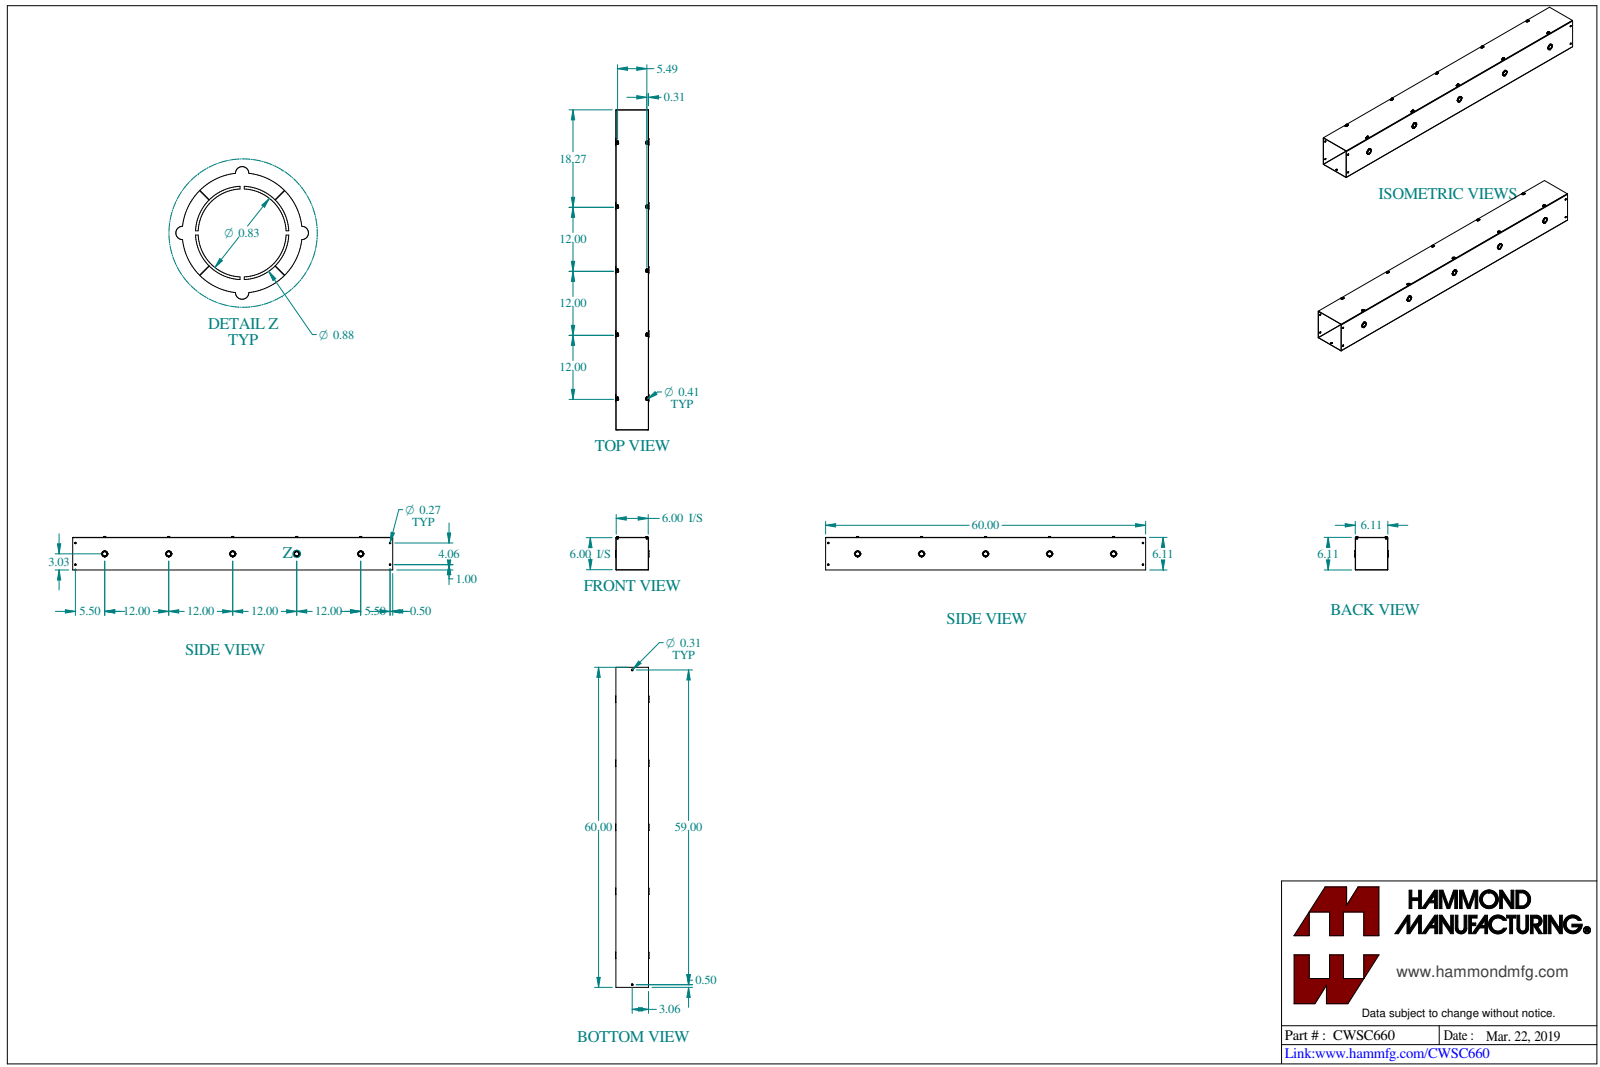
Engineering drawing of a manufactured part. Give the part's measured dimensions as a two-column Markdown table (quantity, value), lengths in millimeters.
| quantity | value |
| --- | --- |
| part name | CWSC660 |
| STEP written by | SolidWorks 2023 (CONFIG_CONTROL_DESIGN) |
| units | millimeters |
| bodies | 12 solids, 786 faces (348 planar, 378 cylindrical, 60 other) |
| overall size | 1524 × 159.7 × 159 |
| volume | 1 410 000 mm³ |
| surface area | 1 947 000 mm² |
| round holes (diameter × count) | 4.5 × 10, 22.2 × 5, 6.8 × 4, 8 × 2 |
| round bosses / shafts (diameter × count) | 9.5 × 10, 4.8 × 10, 28.6 × 5, 21 × 5 |
| partial cylindrical surfaces (radius × count) | 1.6 × 20, 3.2 × 10, 5.2 × 10, 1.6 × 5, 0.7 × 4, 2.2 × 4 |
| main face-to-face distances | 1.4, 153.8, 152.4, 155.3, 151, 2.9, 1.8, 3.3, 155.7, 157.1 |
| hole center spacings | 304.8, 609.6, 335.2, 625.3, 914.4, 139.4, 148.9, 156.1 |
